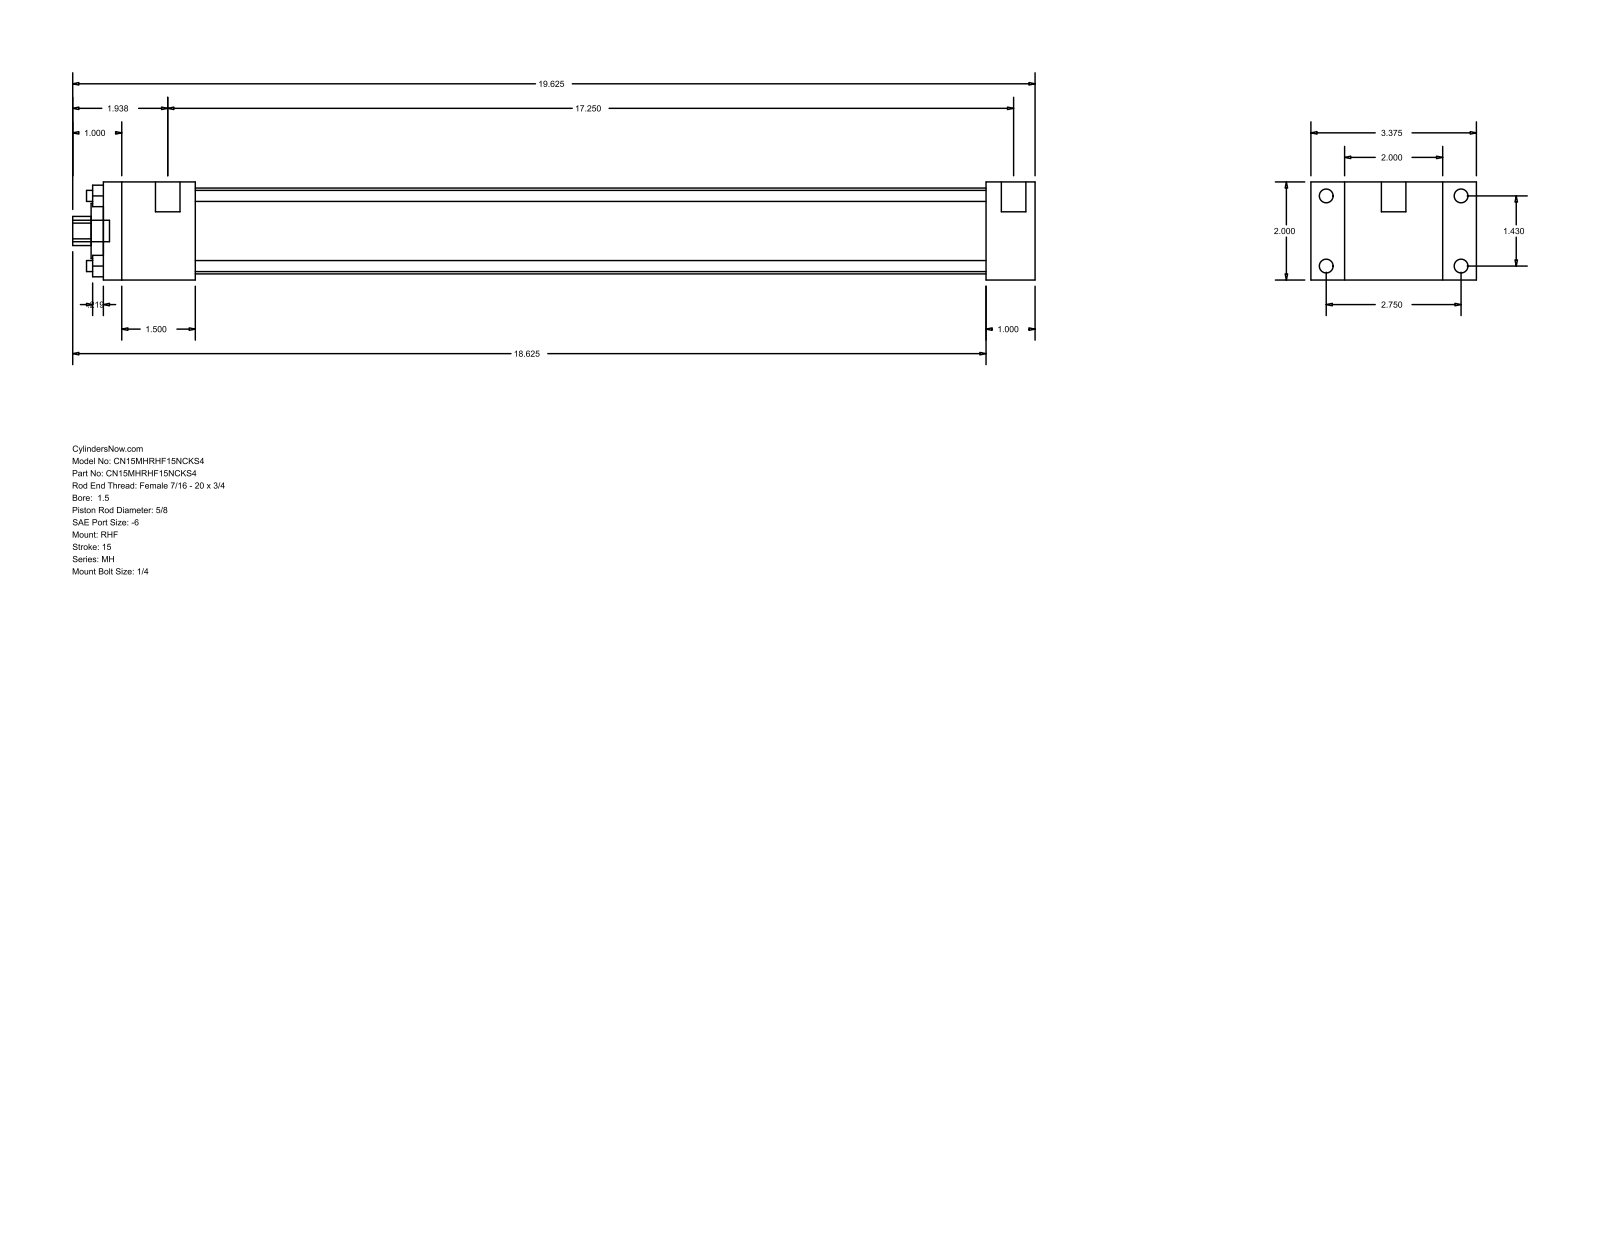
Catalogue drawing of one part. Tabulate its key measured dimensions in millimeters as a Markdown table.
| quantity | value |
| --- | --- |
| part name | MH_RHF__0150_0.625 |
| STEP written by | GSSL Pune (CONFIG_CONTROL_DESIGN) |
| units | millimeters |
| bodies | 0 solids, 88 faces (60 planar, 28 cylindrical, 0 other) |
| overall size | 498.48 × 85.72 × 50.8 |
| round holes (diameter × count) | 5.71 × 4, 15.88 × 1, 28.57 × 1, 44.45 × 1 |
| round bosses / shafts (diameter × count) | 7.14 × 4, 5.56 × 4, 12.7 × 2, 11.11 × 1 |
| partial cylindrical surfaces (radius × count) | 7.54 × 1 |
| main face-to-face distances | 50.8, 17.46, 68.26, 25.41, 457.19, 482.6, 85.72, 47.62, 409.57, 434.98 |
| hole center spacings | 25.68, 36.32, 51.36 |
